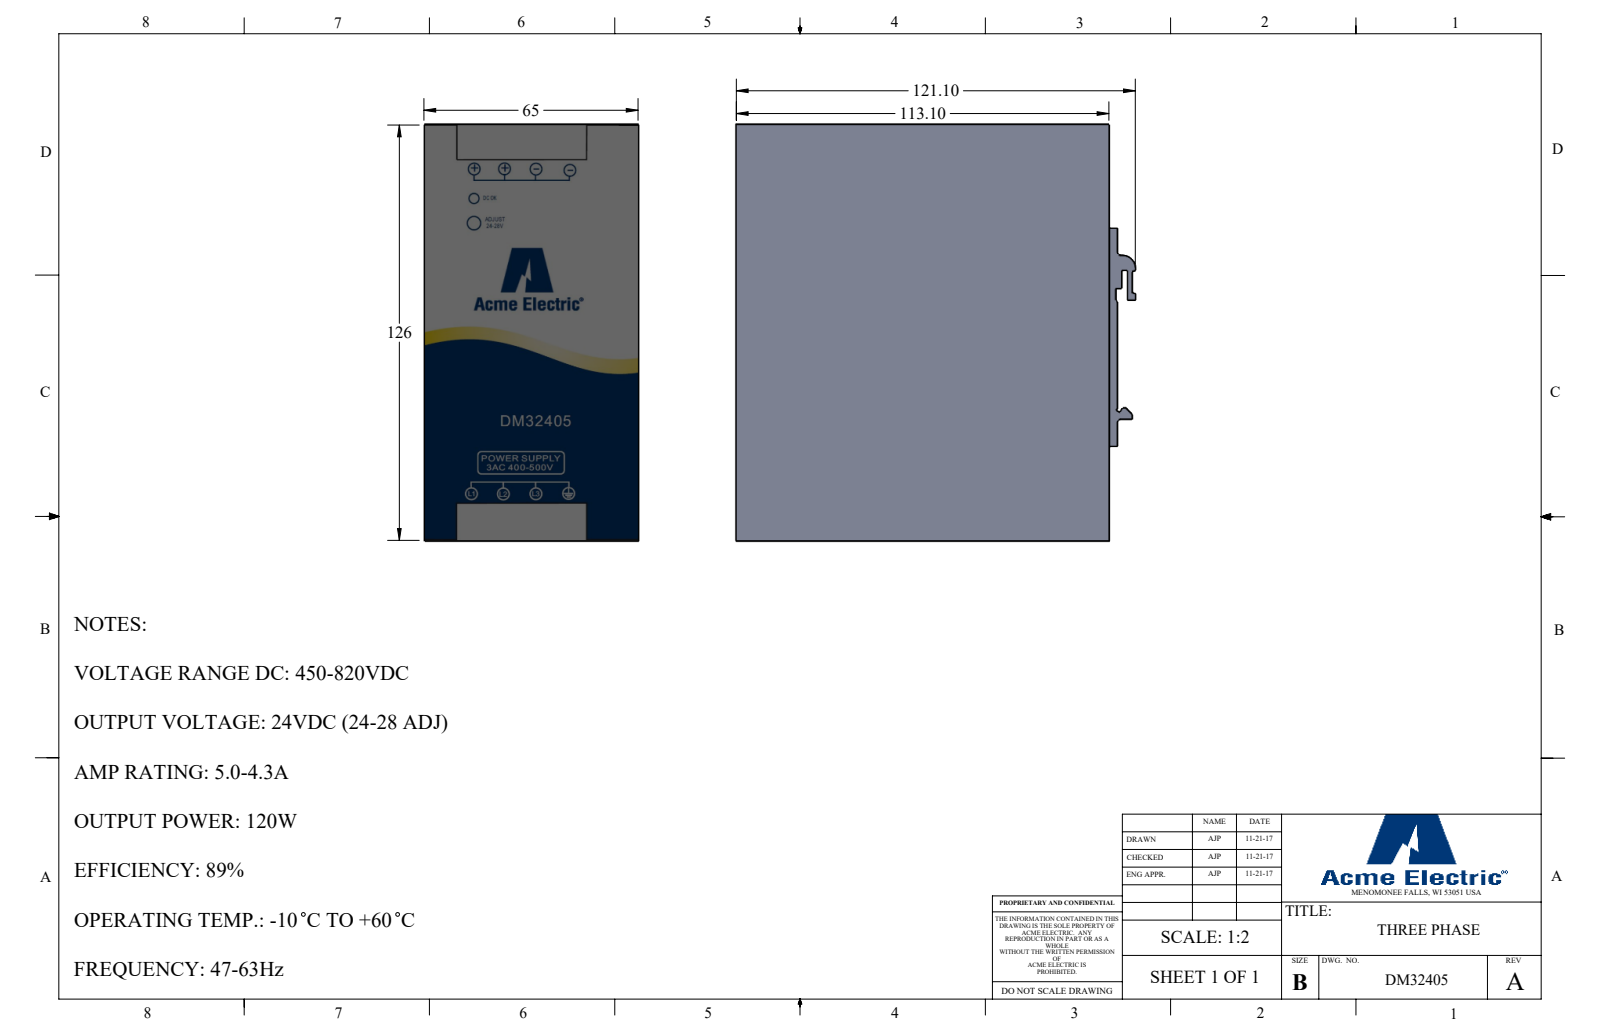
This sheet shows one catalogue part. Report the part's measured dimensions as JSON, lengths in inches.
{"part_name": "DM32405", "step_written_by": "SolidWorks 2017 (AUTOMOTIVE_DESIGN)", "units": "inches", "bodies": {"solids": 1, "faces": 36, "planar": 33, "cylindrical": 3, "other": 0}, "overall_size": [4.961, 4.768, 2.559], "volume_in3": 57.15, "surface_area_in2": 96.15, "partial_cylinders_radius": [[0.039, 2], [0.157, 1]], "face_to_face_distances": [2.559, 4.961, 4.453, 0.098, 4.551, 0.217, 0.374, 2.185, 0.118, 4.669]}
